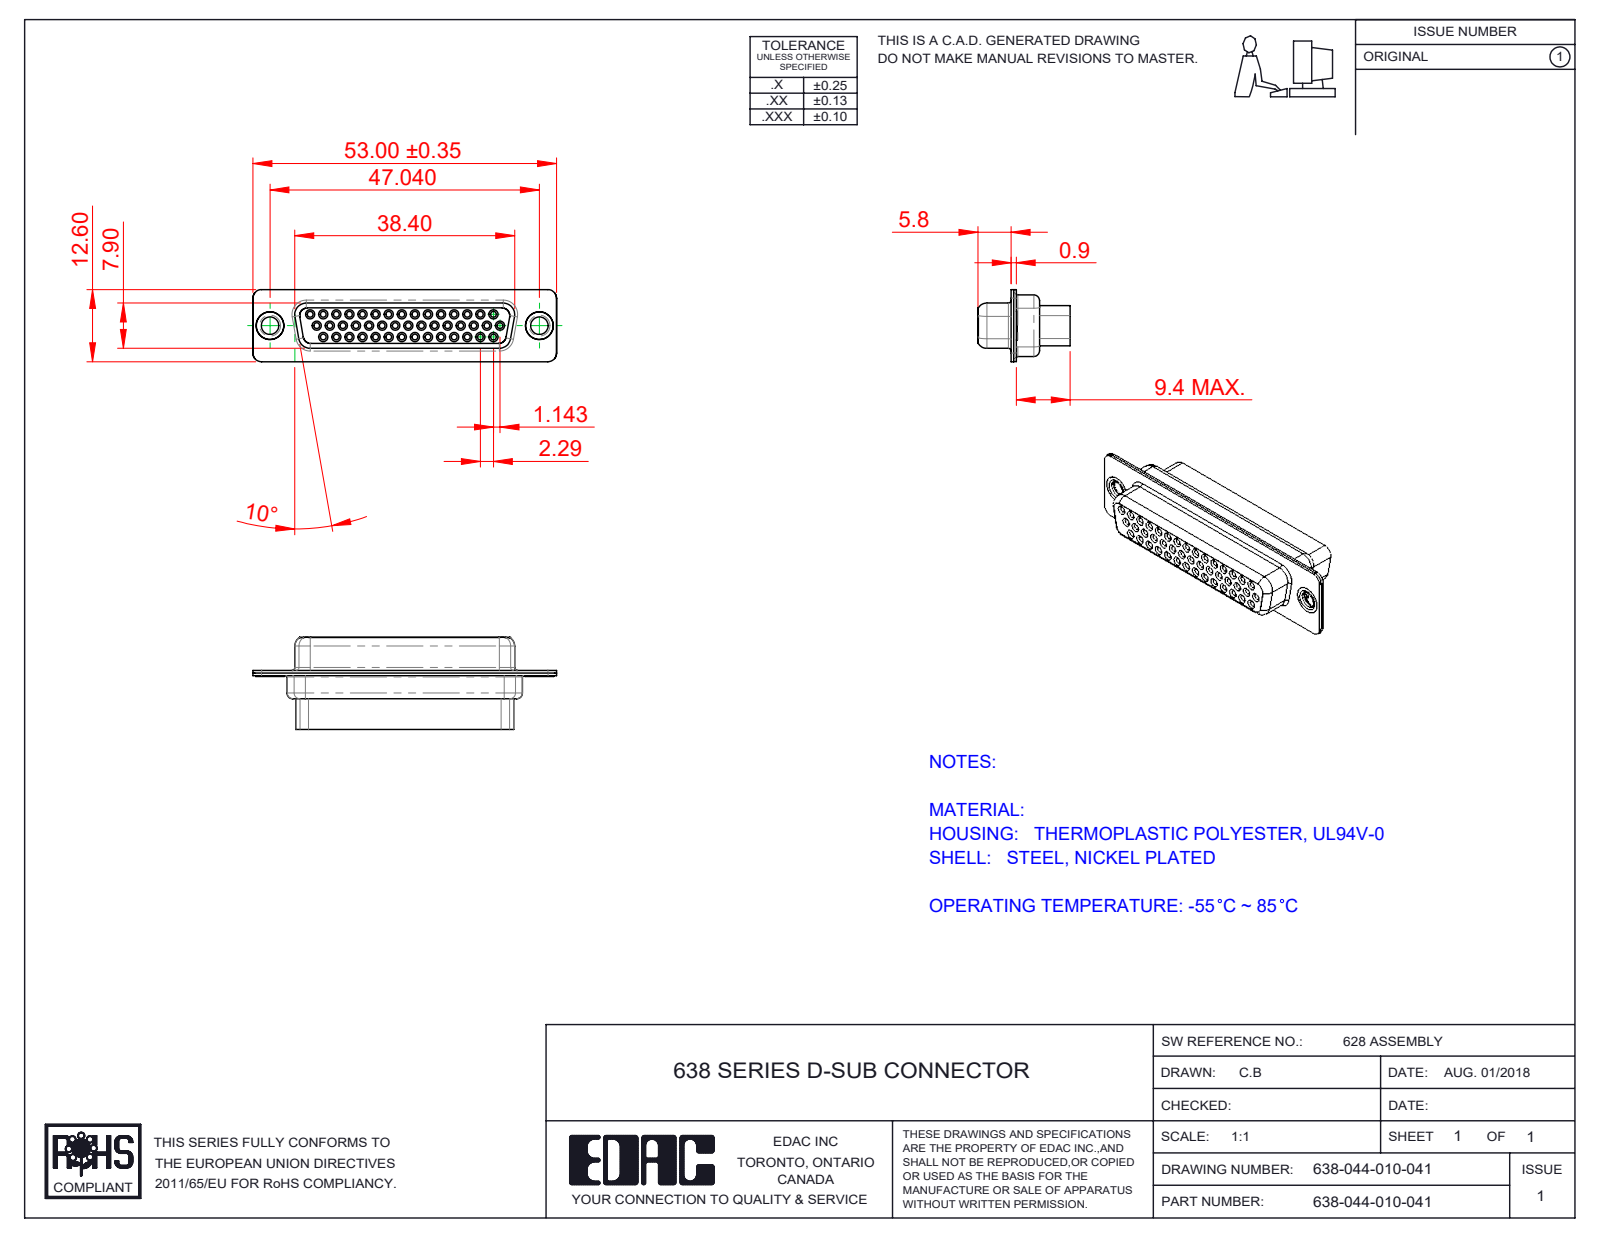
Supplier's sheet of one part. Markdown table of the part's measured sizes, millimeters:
| quantity | value |
| --- | --- |
| part name | 638-044-010-041; 638 Thru Hole Rivet; 638 Shell Rear_44 Contacts; 638 Shell Front_44 Contacts (+1 more) |
| STEP written by | SolidWorks 2020 (CONFIG_CONTROL_DESIGN) |
| units | millimeters |
| bodies | 5 solids, 825 faces (199 planar, 473 cylindrical, 153 other) |
| overall size | 53.04 × 16.1 × 12.6 |
| volume | 3 399 mm³ |
| surface area | 9 395 mm² |
| round holes (diameter × count) | 1 × 44, 1.7 × 44, 1.8 × 44, 2 × 44, 3.05 × 2, 4 × 2, 4.05 × 2, 4.85 × 2 |
| round bosses / shafts (diameter × count) | 5 × 2, 4.95 × 2, 4.8 × 2, 3.55 × 2 |
| partial cylindrical surfaces (radius × count) | 1.5 × 20, 2 × 12, 1.55 × 8, 0.25 × 4, 0.5 × 4, 0.55 × 4, 0.7 × 4, 0.95 × 4 |
| main face-to-face distances | 0.45, 0.4, 6.6, 1.43, 8.88, 7, 0.9, 0.85, 7.05, 7.45 |
| hole center spacings | 2.28, 2.29, 3.96, 4.57, 8.24, 6.86, 11.43, 10.48 |
